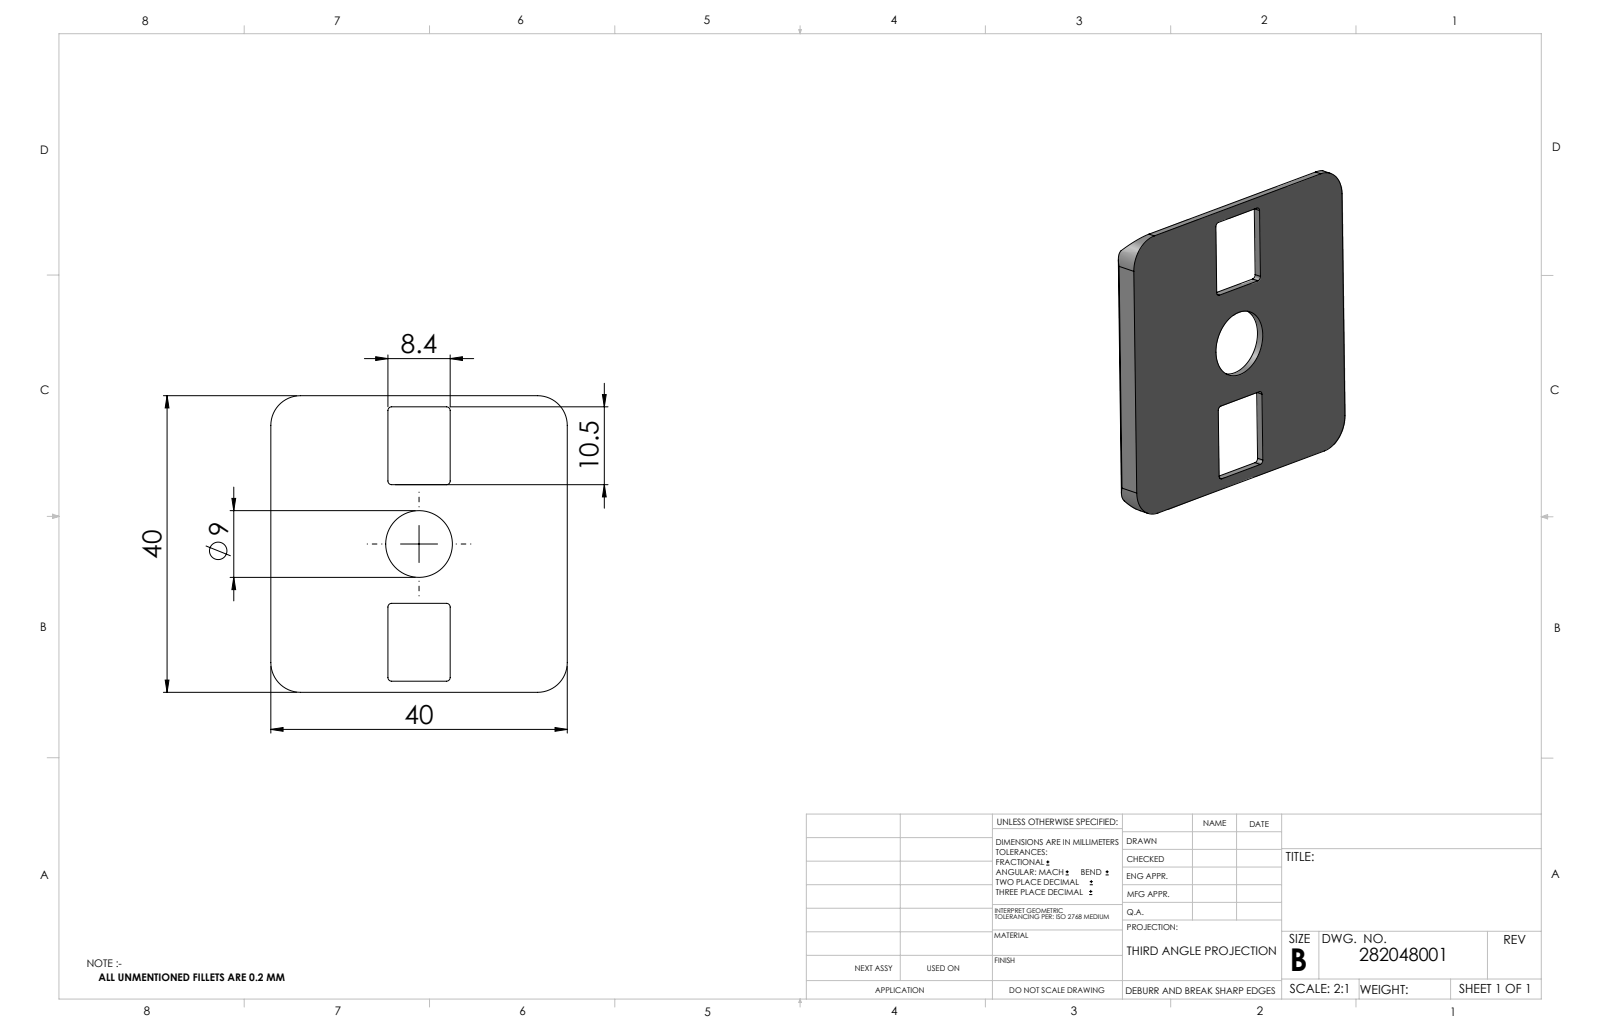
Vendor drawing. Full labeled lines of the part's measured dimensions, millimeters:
Part name (STEP PRODUCT): 282048001_c_1
STEP written by: SolidWorks 2014 (CONFIG_CONTROL_DESIGN)
Units: millimetres
Bodies: 1 solid, 34 faces (14 planar, 20 cylindrical, 0 other)
Overall size (bounding box): 40 × 40 × 3.1
Volume: 1 575 mm³ · Surface area: 3 160 mm²
Round holes (diameter × count): ⌀9 ×1
Partial cylindrical surfaces — rounded edges, fillets, slot ends (radius × count): R0.5 ×8, R4 ×6, R0.3 ×2
Main face-to-face distances: 1, 40, 15.8, 24.2, 8.4, 12, 28, 1.5, 38.5, 10.5
